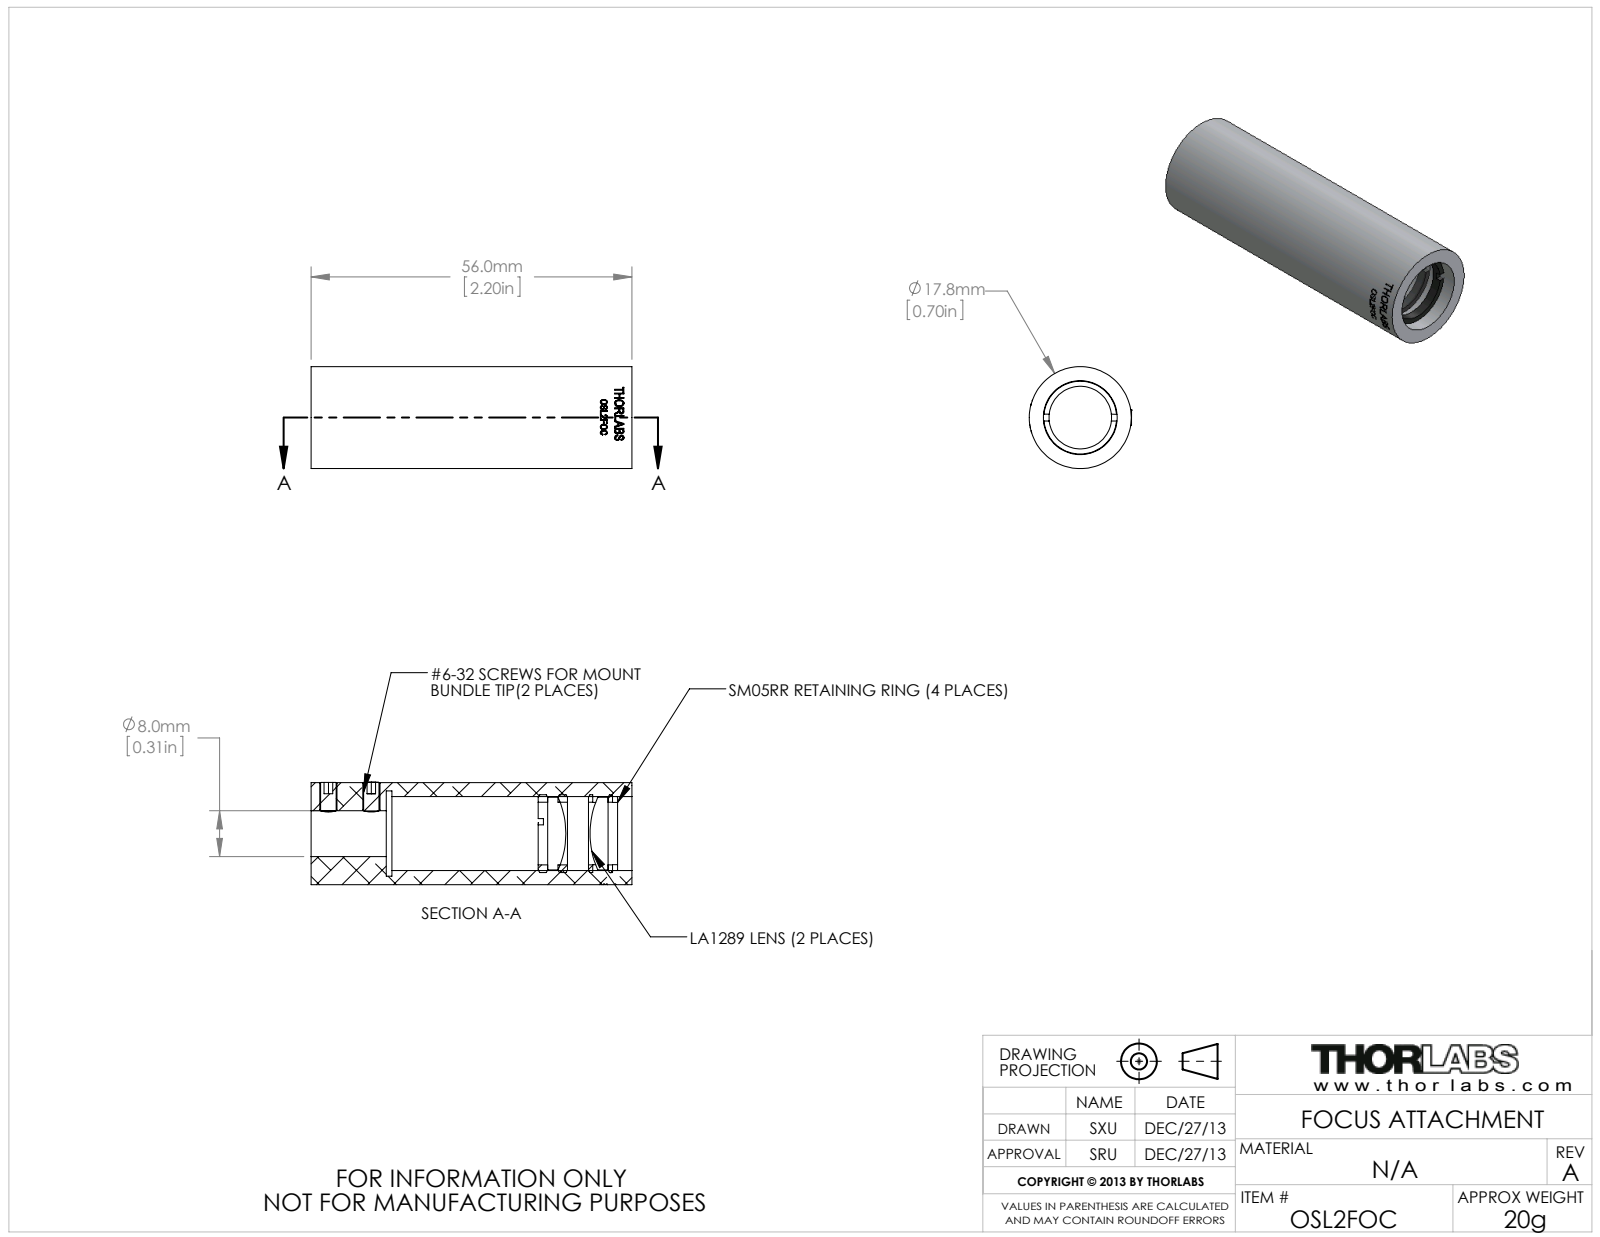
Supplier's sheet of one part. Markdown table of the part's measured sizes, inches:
| quantity | value |
| --- | --- |
| part name | OSL2FOC |
| STEP written by | SolidWorks 2012 (CONFIG_CONTROL_DESIGN) |
| units | inches |
| bodies | 1 solid, 223 faces (72 planar, 40 cylindrical, 111 other) |
| overall size | 2.205 × 0.701 × 0.701 |
| volume | 0.462 in³ |
| surface area | 8.93 in² |
| round holes (diameter × count) | 0.107 × 2, 0.315 × 1, 0.508 × 1, 0.587 × 1 |
| round bosses / shafts (diameter × count) | 0.701 × 1 |
| partial cylindrical surfaces (radius × count) | 0.346 × 1 |
| main face-to-face distances | 0.516, 2.205, 1.689, 0.555, 0.039, 1.65, 2.15, 1.634, 1.594, 0.055 |
